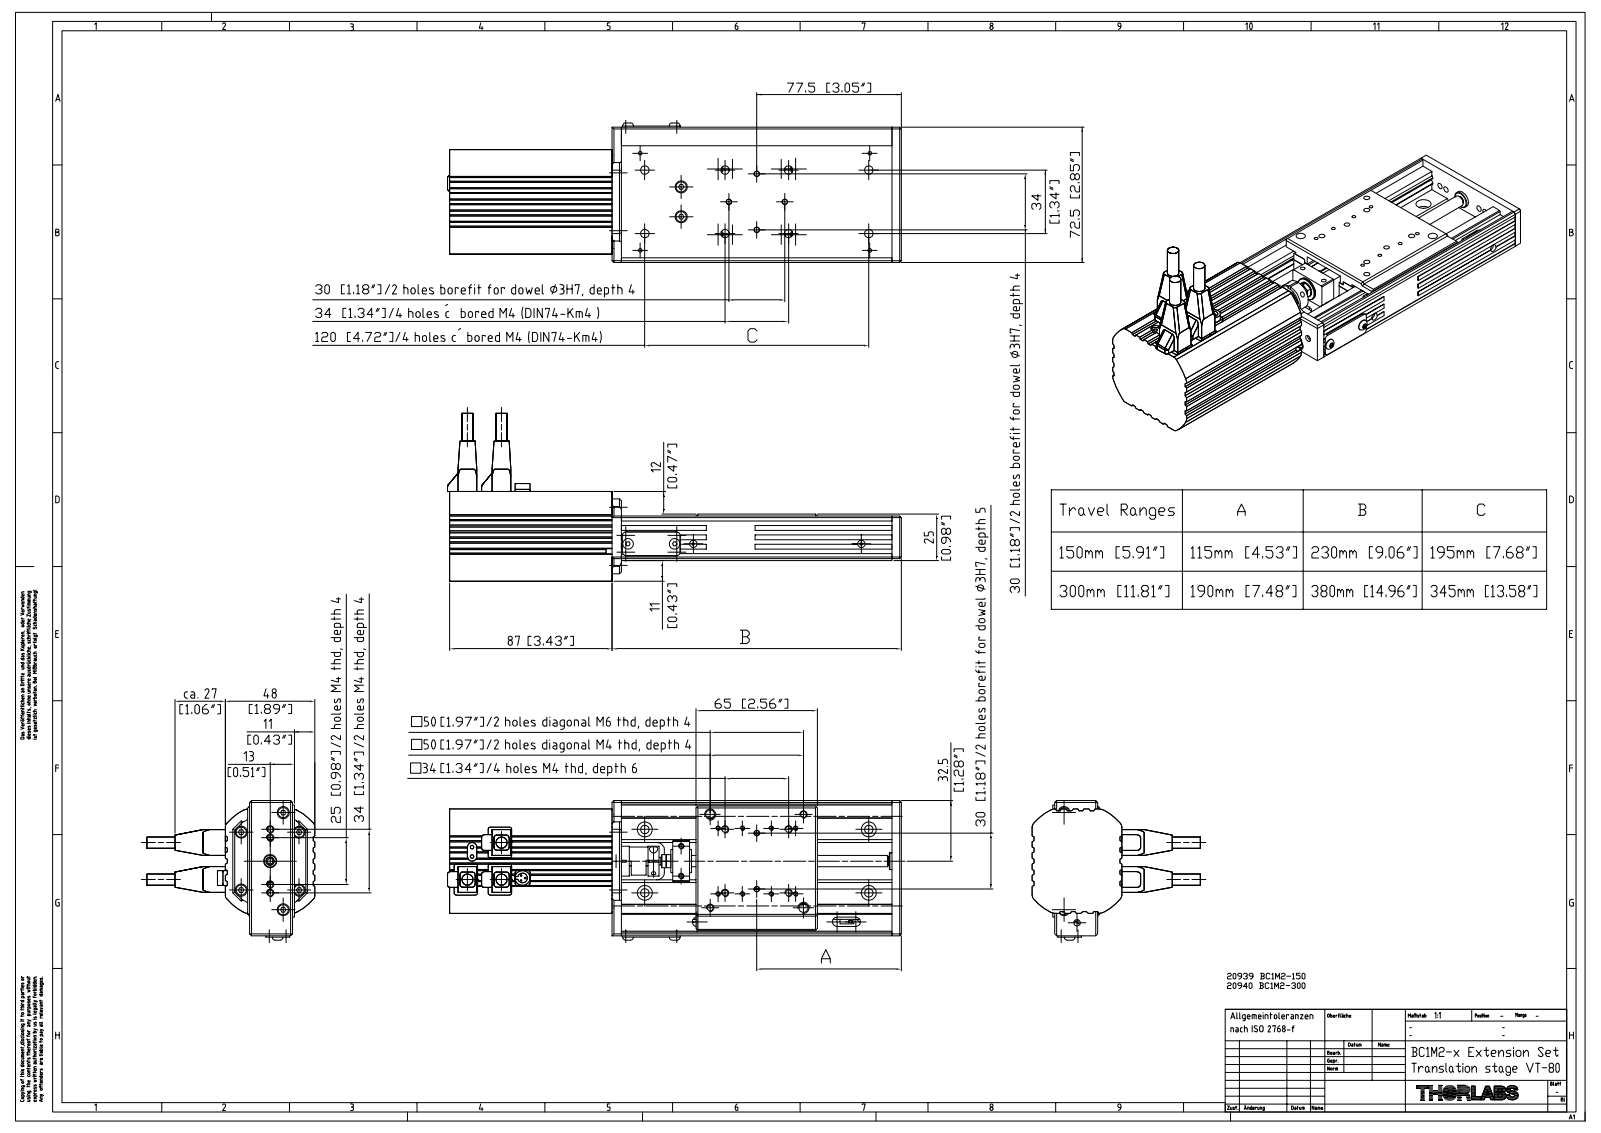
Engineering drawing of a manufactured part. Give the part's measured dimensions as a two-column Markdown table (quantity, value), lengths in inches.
| quantity | value |
| --- | --- |
| part name | 20939-E0W |
| STEP written by | SolidWorks 2010 (CONFIG_CONTROL_DESIGN) |
| units | inches |
| bodies | 1 solid, 63 faces (30 planar, 33 cylindrical, 0 other) |
| overall size | 3.504 × 2.815 × 1.811 |
| volume | 5.819 in³ |
| surface area | 34.28 in² |
| round holes (diameter × count) | 0.118 × 2, 0.197 × 2, 0.433 × 2, 0.169 × 1, 0.248 × 1, 0.252 × 1, 0.315 × 1 |
| partial cylindrical surfaces (radius × count) | 0.394 × 4, 0.197 × 2, 0.315 × 2, 0.472 × 2, 0.531 × 2, 1.476 × 1 |
| main face-to-face distances | 0.472, 1.043, 1.114, 0.642, 2.854, 2.815, 1.772, 0.039, 1.004, 2.776 |
| hole center spacings | 1.06, 1.303, 1.857, 2.361, 1.181, 1.969 |
